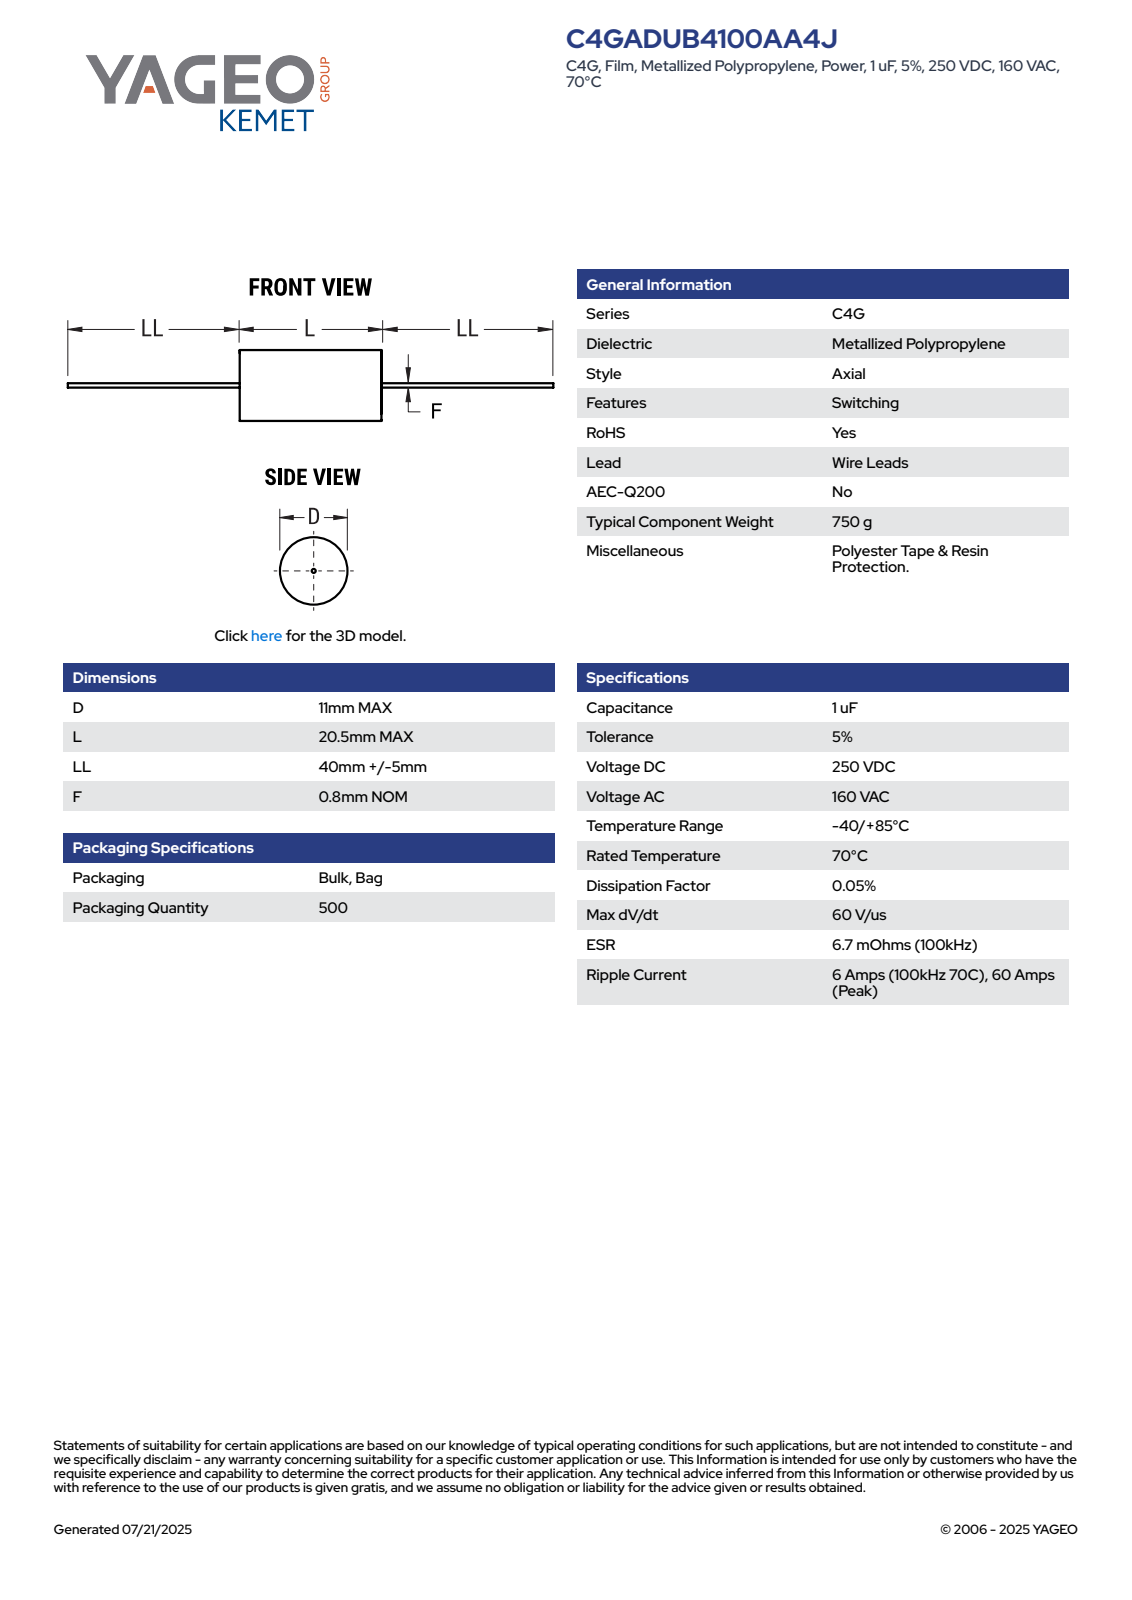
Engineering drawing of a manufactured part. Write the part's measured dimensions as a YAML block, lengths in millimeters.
part_name: "CFP_ACWF_11X20.5_D11L20.5LL45F0.8"
step_written_by: "SolidWorks 2014 (AUTOMOTIVE_DESIGN)"
units: millimeters
bodies: {solids: 2, faces: 87, planar: 28, cylindrical: 28, other: 31}
overall_size: [110.5, 11, 11]
volume: 1993
surface_area: 1315
round_bosses_or_shafts:
  - {diameter: 11, count: 1}
  - {diameter: 0.8, count: 1}
partial_cylinders:
  - {radius: 5.49, count: 1}
face_to_face_distances: [20.51, 20.5, 45, 65.5, 44.99, 110.5, 65.51]
